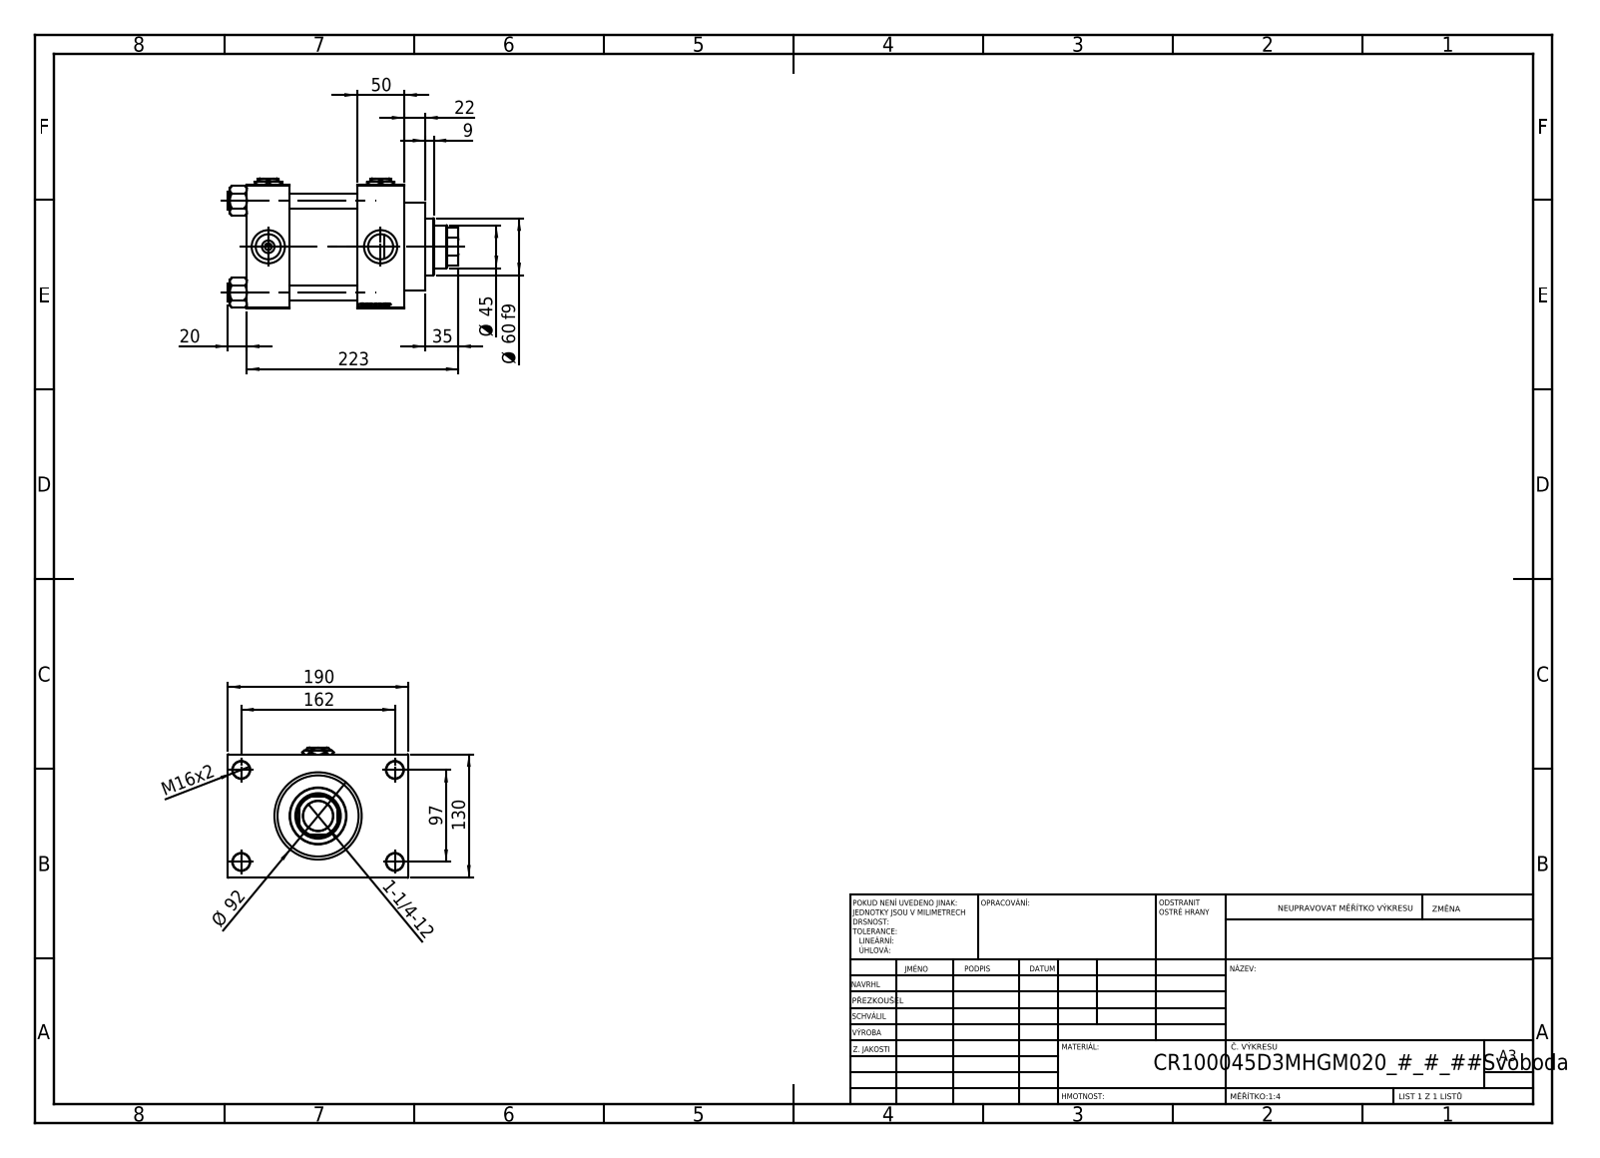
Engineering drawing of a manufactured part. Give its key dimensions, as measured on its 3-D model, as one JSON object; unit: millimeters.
{"part_name": "NUT_M5_D; V215_VC_A; V215CR_D_Body; V215CR_VCP_D (+2 more)", "step_written_by": "SolidWorks 2019 (CONFIG_CONTROL_DESIGN)", "units": "millimeters", "bodies": {"solids": 13, "faces": 1252, "planar": 593, "cylindrical": 99, "other": 560}, "overall_size": [243, 190, 137], "volume_mm3": 2576000, "surface_area_mm2": 361795, "round_holes": [[16, 4], [18, 4], [26.44, 4], [35, 4], [7, 3], [31.5, 1], [45, 1], [48, 1], [76, 1], [85.5, 1], [100, 1]], "round_bosses_or_shafts": [[19, 4], [106, 1], [92, 1], [60, 1]], "partial_cylinders_radius": [[22, 1]], "face_to_face_distances": [45, 130, 116, 71, 166, 121, 50, 30, 160, 20], "hole_center_spacings": [32.55, 68.52, 94.41, 96.9, 102.27, 129.45, 161.73, 97]}
